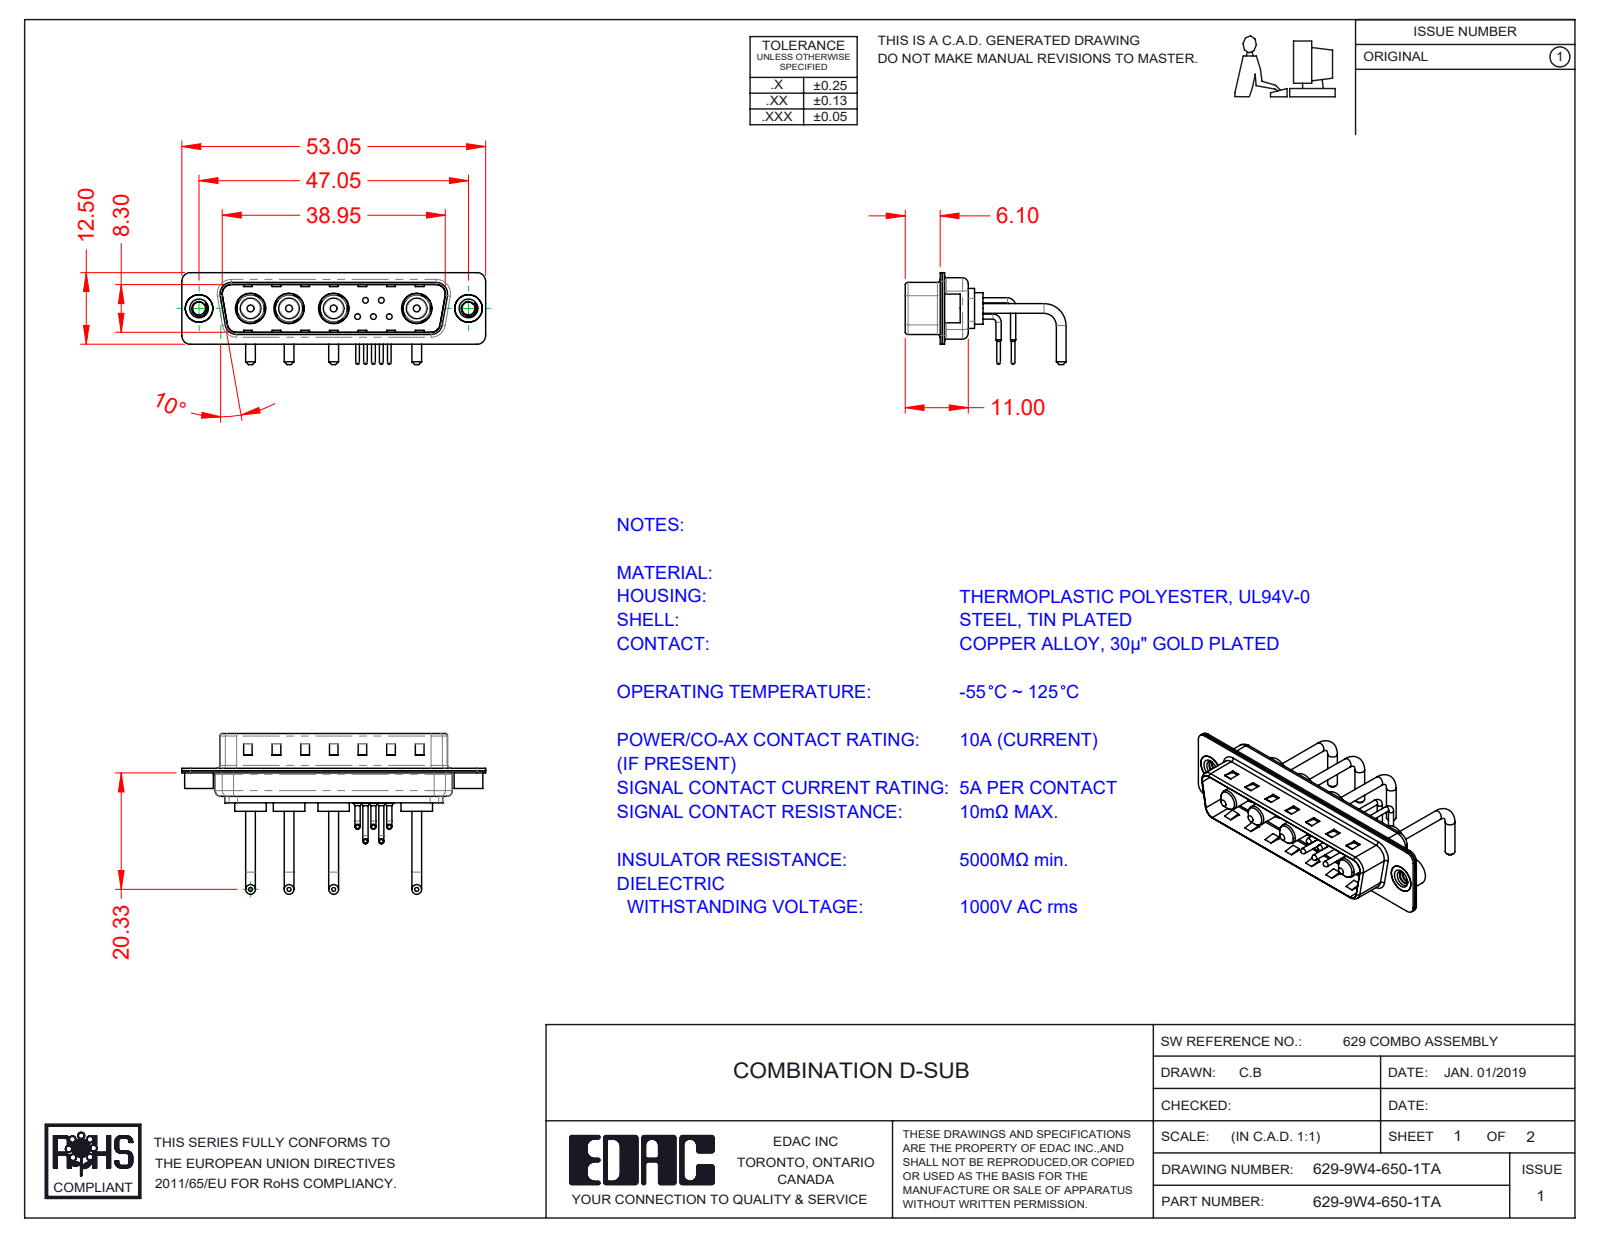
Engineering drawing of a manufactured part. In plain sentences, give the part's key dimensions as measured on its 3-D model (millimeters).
The part is named "629Combo Threaded Rivet_2; 629Combo Shell Front_25 Contacts; Power Pin_Ext 10A RA; 629Combo Shell Rear_25 Contacts (+4 more)". Its 3-D file was written by "SolidWorks 2020 (CONFIG_CONTROL_DESIGN)". It is 18 solids with 1098 faces: 531 planar, 401 cylindrical and 166 other. Overall it measures 53.05 by 28.08 by 16.05 millimeters. Its volume is 3 138 cubic millimeters and its surface area 7 200 square millimeters. Round holes: 5 of diameter 0.75, 5 of diameter 1.6, 5 of diameter 2, 4 of diameter 4.85, 4 of diameter 5.3, 2 of diameter 2.26, 2 of diameter 4, 2 of diameter 4.8. Round bosses or shafts: 10 of diameter 0.9, 8 of diameter 1.7, 5 of diameter 1.5, 5 of diameter 1, 5 of diameter 0.65, 4 of diameter 5.5, 4 of diameter 5.2, 4 of diameter 4.75. Partial cylindrical surfaces (rounded edges, fillets, slot ends): 16 of radius 1.5, 12 of radius 2, 8 of radius 0.5, 8 of radius 1.6, 5 of radius 1.01, 4 of radius 0.25, 4 of radius 0.6, 4 of radius 0.65. The main face-to-face distances are 0.4, 0.8, 9.5, 9.1, 8.7, 9.9, 0.75, 1.2, 5.6, 0.35. The hole center spacings are 3.16, 2.77, 5.04, 14.5, 2.78, 4.4, 4.41, 5.
